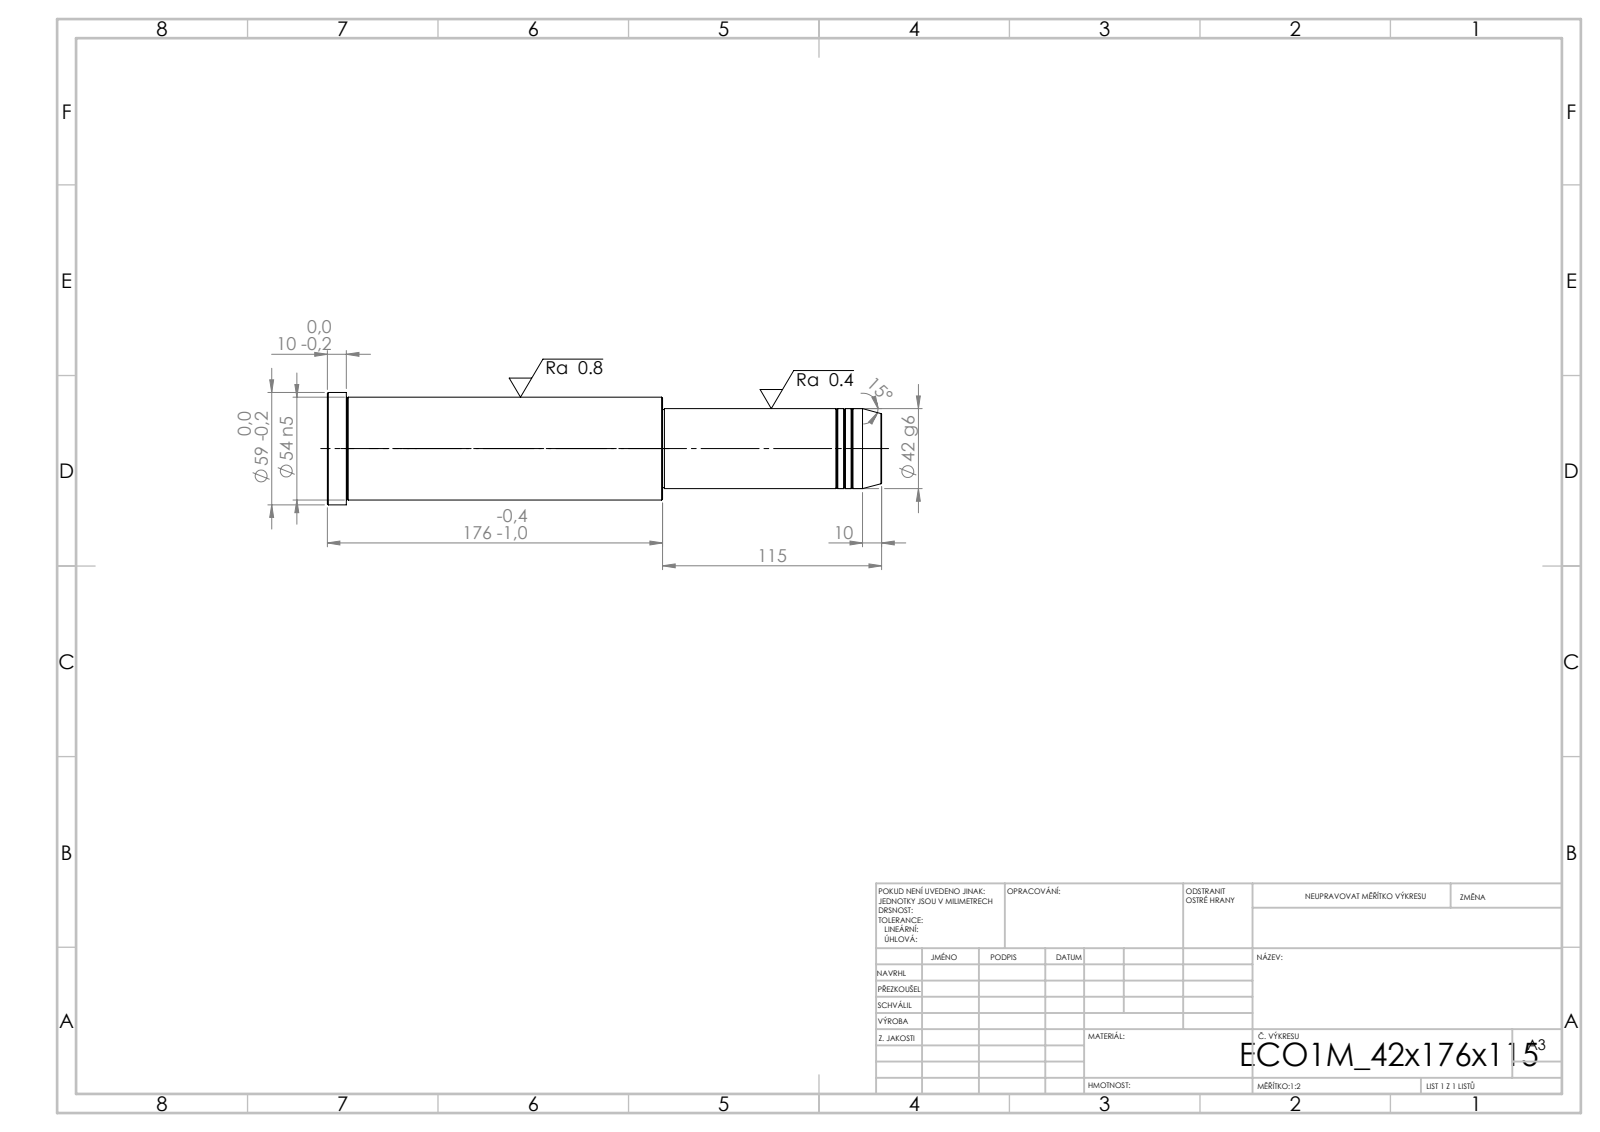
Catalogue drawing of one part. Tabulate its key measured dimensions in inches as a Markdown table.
| quantity | value |
| --- | --- |
| STEP written by | SolidWorks 2019 (CONFIG_CONTROL_DESIGN) |
| units | inches |
| bodies | 1 solid, 43 faces (5 planar, 14 cylindrical, 24 other) |
| overall size | 11.457 × 2.323 × 2.323 |
| volume | 34.47 in³ |
| surface area | 78.44 in² |
| round bosses / shafts (diameter × count) | 2.323 × 1, 2.126 × 1, 1.654 × 1, 1.614 × 1 |
| main face-to-face distances | 11.457, 4.528, 6.929, 11.063, 6.535, 0.394, 4.488, 0.039, 6.575, 6.969 |
